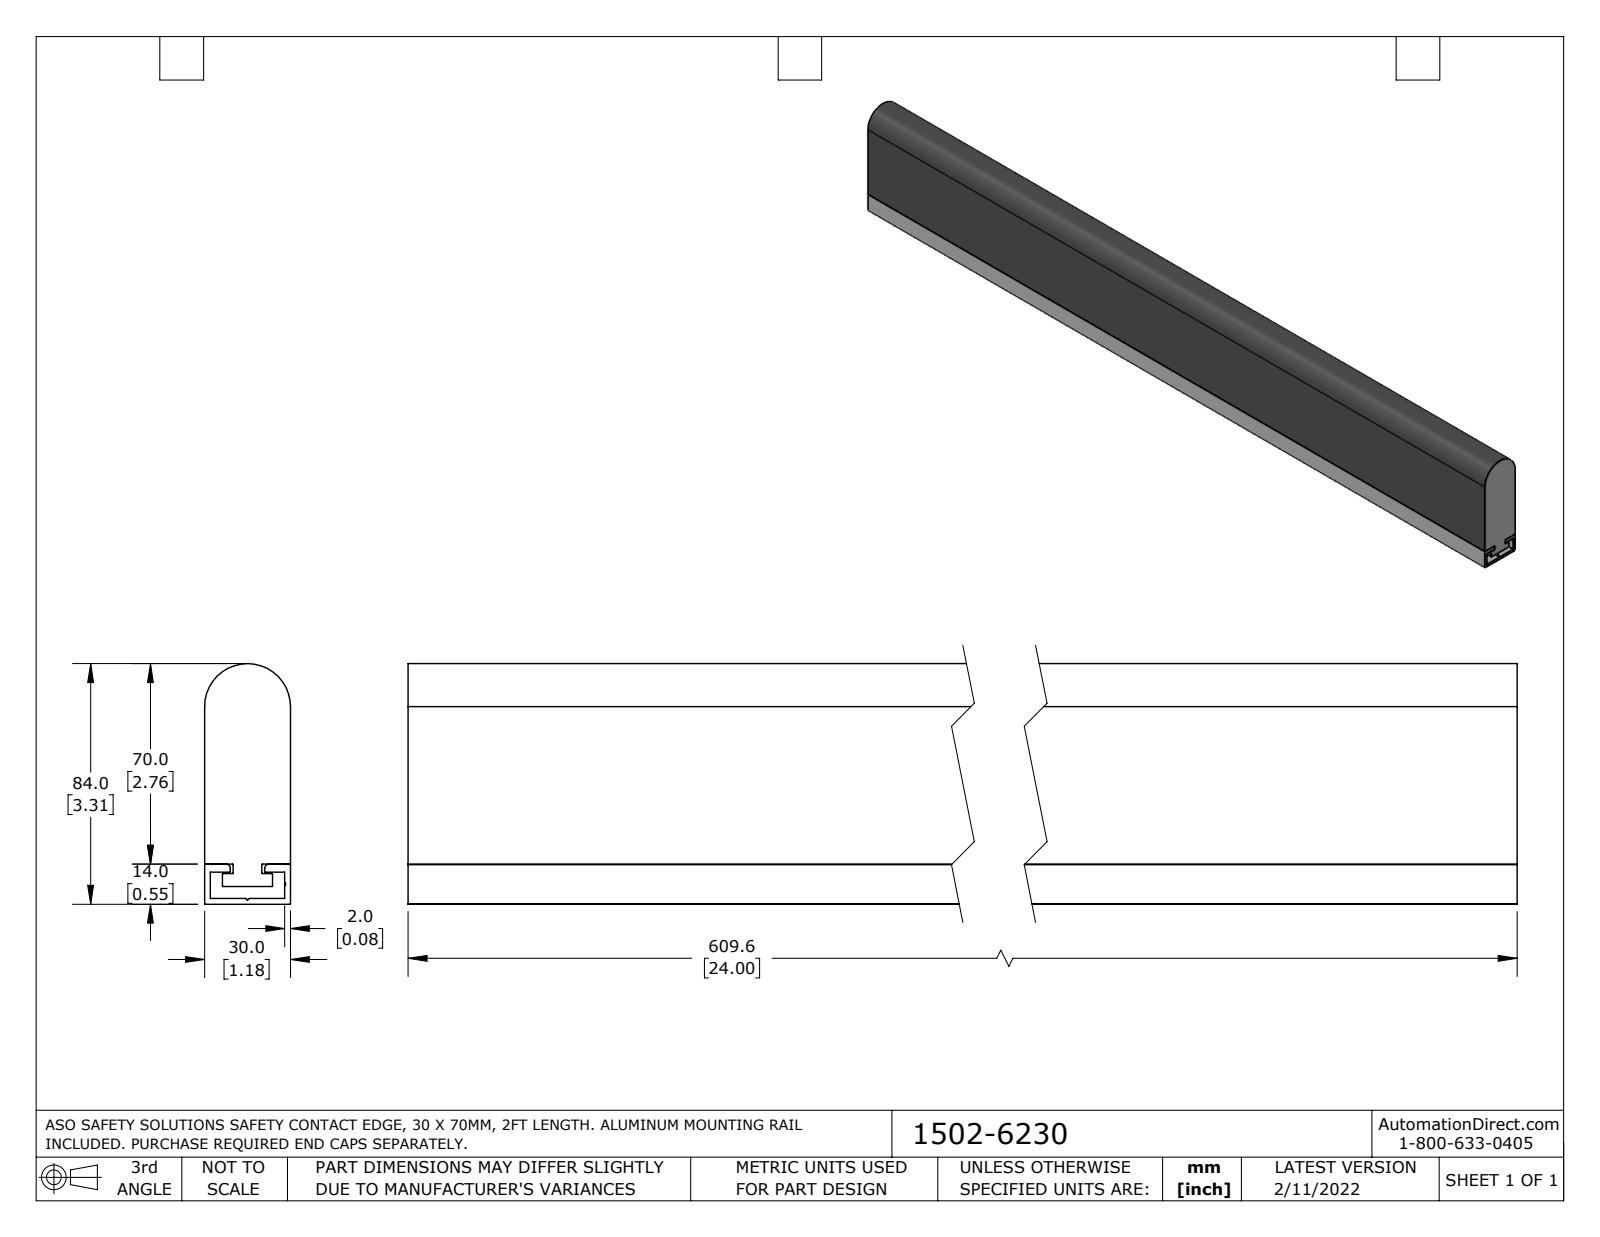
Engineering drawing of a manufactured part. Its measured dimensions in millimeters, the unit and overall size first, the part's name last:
Units: millimetres
Overall size (bounding box): 609.6 × 84 × 30
Partial cylindrical surfaces — rounded edges, fillets, slot ends (radius × count): R0.2 ×12, R1.5 ×2, R15 ×1
Main face-to-face distances: 30, 2, 14, 12, 28, 6.2, 4.2, 7.8, 11.2, 9.2
Volume: 1 378 000 mm³ · Surface area: 221 800 mm²
Bodies: 2 solids, 50 faces (35 planar, 15 cylindrical, 0 other)
Part name (STEP PRODUCT): 1502-6230_Default
STEP written by: SolidWorks 2021 (CONFIG_CONTROL_DESIGN)
